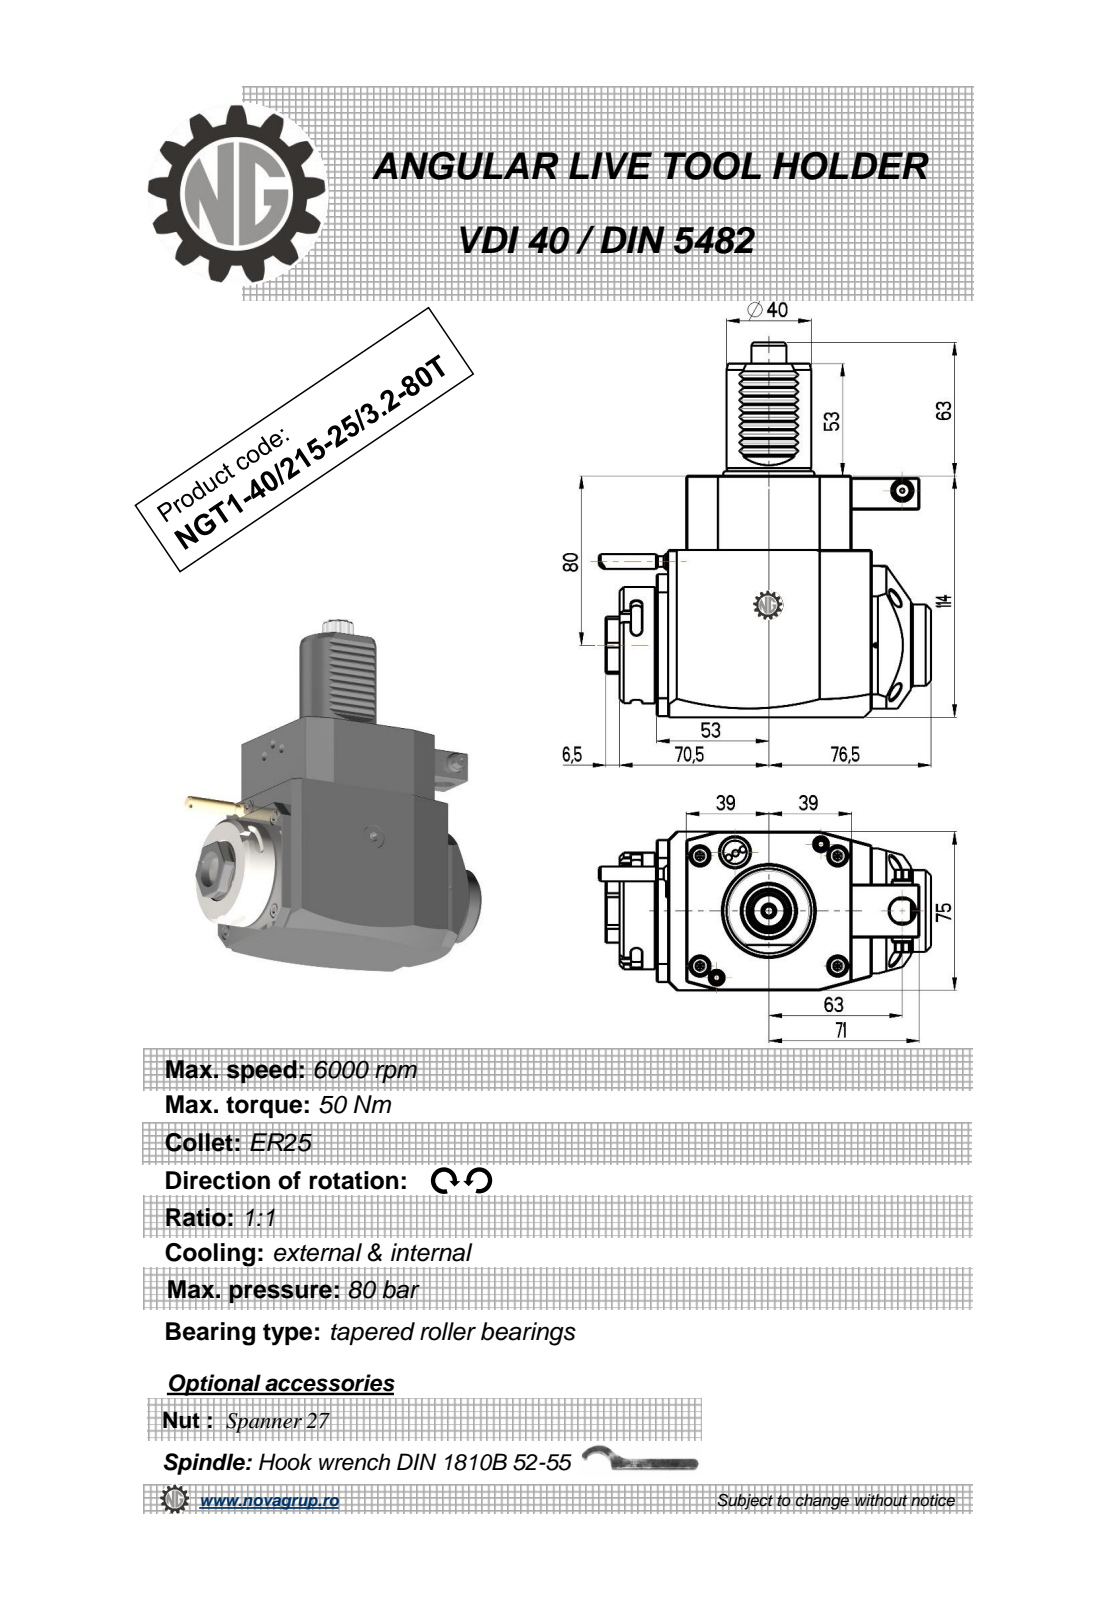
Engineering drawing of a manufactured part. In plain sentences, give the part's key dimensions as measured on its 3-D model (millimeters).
The part is named "NGT1_40_215_25_3_2_80T". Its 3-D file was written by "PRO/ENGINEER BY PARAMETRIC TECHNOLOGY CORPORATION, 2010280 (CONFIG_CONTROL_DESIGN)". It is 1 solid with 394 faces: 176 planar, 125 cylindrical and 93 other. Overall it measures 177 by 156.83 by 75 millimeters. Its volume is 957 780 cubic millimeters and its surface area 71 135 square millimeters. Round holes: 1 of diameter 2, 1 of diameter 2.5, 1 of diameter 3, 1 of diameter 4.2, 1 of diameter 5.3, 1 of diameter 9.5, 1 of diameter 12, 1 of diameter 18. Round bosses or shafts: 2 of diameter 8, 1 of diameter 55, 1 of diameter 48, 1 of diameter 40, 1 of diameter 38.5, 1 of diameter 10, 1 of diameter 7, 1 of diameter 5. Partial cylindrical surfaces (rounded edges, fillets, slot ends): 18 of radius 3.03, 10 of radius 0.3, 6 of radius 2.5, 2 of radius 180, 1 of radius 0.5, 1 of radius 3.85, 1 of radius 4.25, 1 of radius 6.75. The main face-to-face distances are 75, 114, 14, 17.5, 92, 78, 109.5, 31.5, 35, 79. The hole center spacings are 37.35, 43.2, 63, 72.5.
